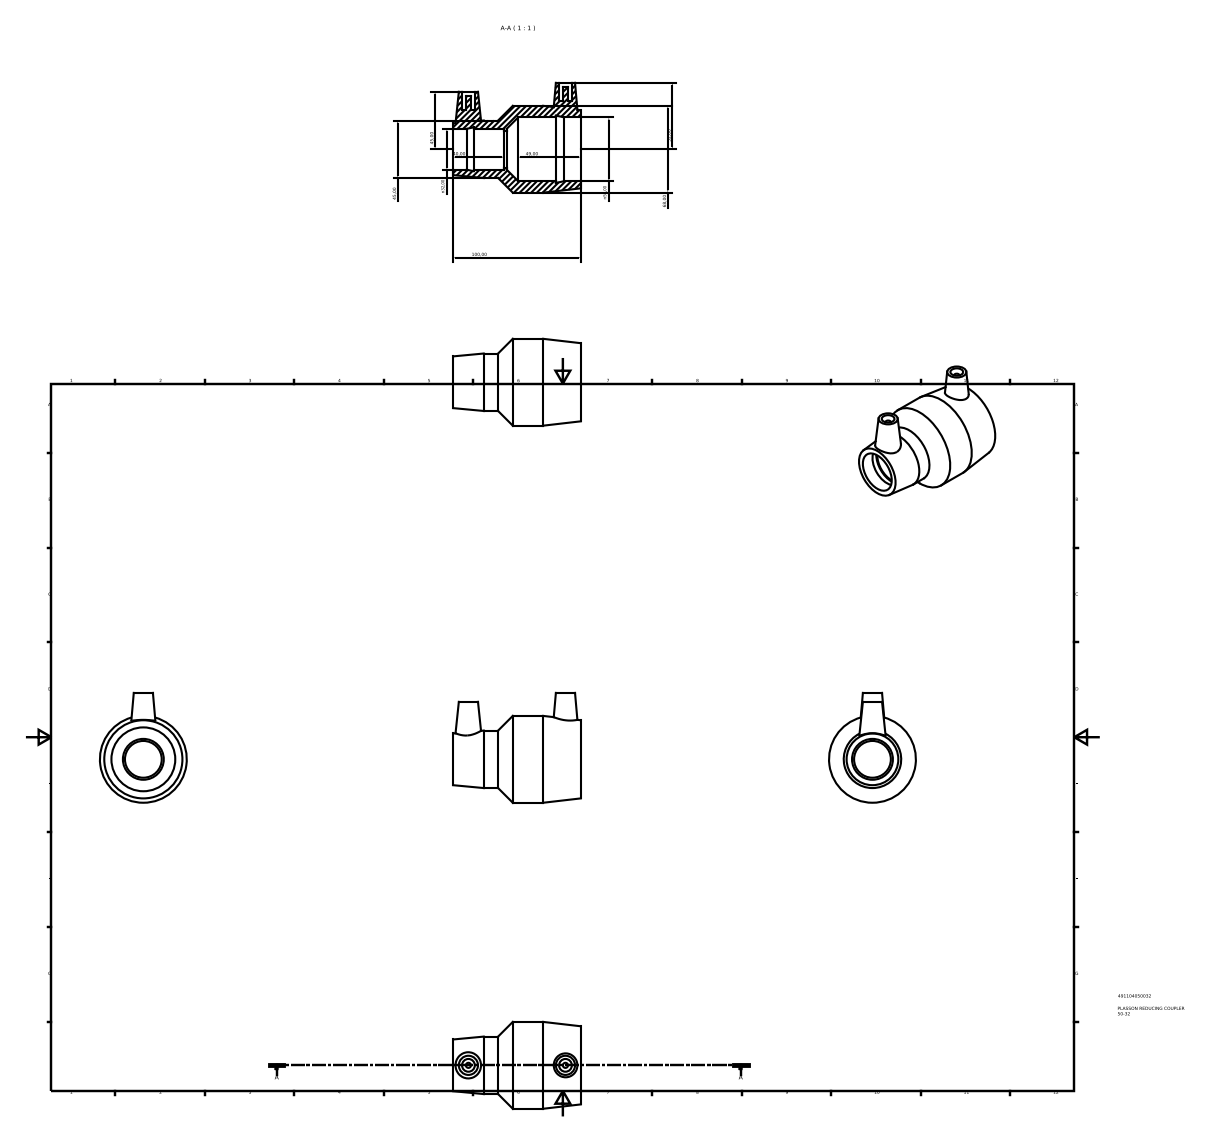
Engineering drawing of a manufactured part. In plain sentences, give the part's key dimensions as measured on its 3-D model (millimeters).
The part is named "491104050032". Its 3-D file was written by "Autodesk Inventor 2015 (AUTOMOTIVE_DESIGN)". It is 1 solid with 31 faces: 12 planar, 11 cylindrical and 8 other. Overall it measures 100 by 86 by 68 millimeters. Its volume is 130 383 cubic millimeters and its surface area 37 932 square millimeters. Round holes: 2 of diameter 10, 1 of diameter 28.8, 1 of diameter 32, 1 of diameter 50. Round bosses or shafts: 2 of diameter 4, 1 of diameter 68, 1 of diameter 45. The main face-to-face distances are 100, 7, 80.4, 19.6, 42, 38.4, 58, 40, 2, 40.4. The hole center spacings are 76.
